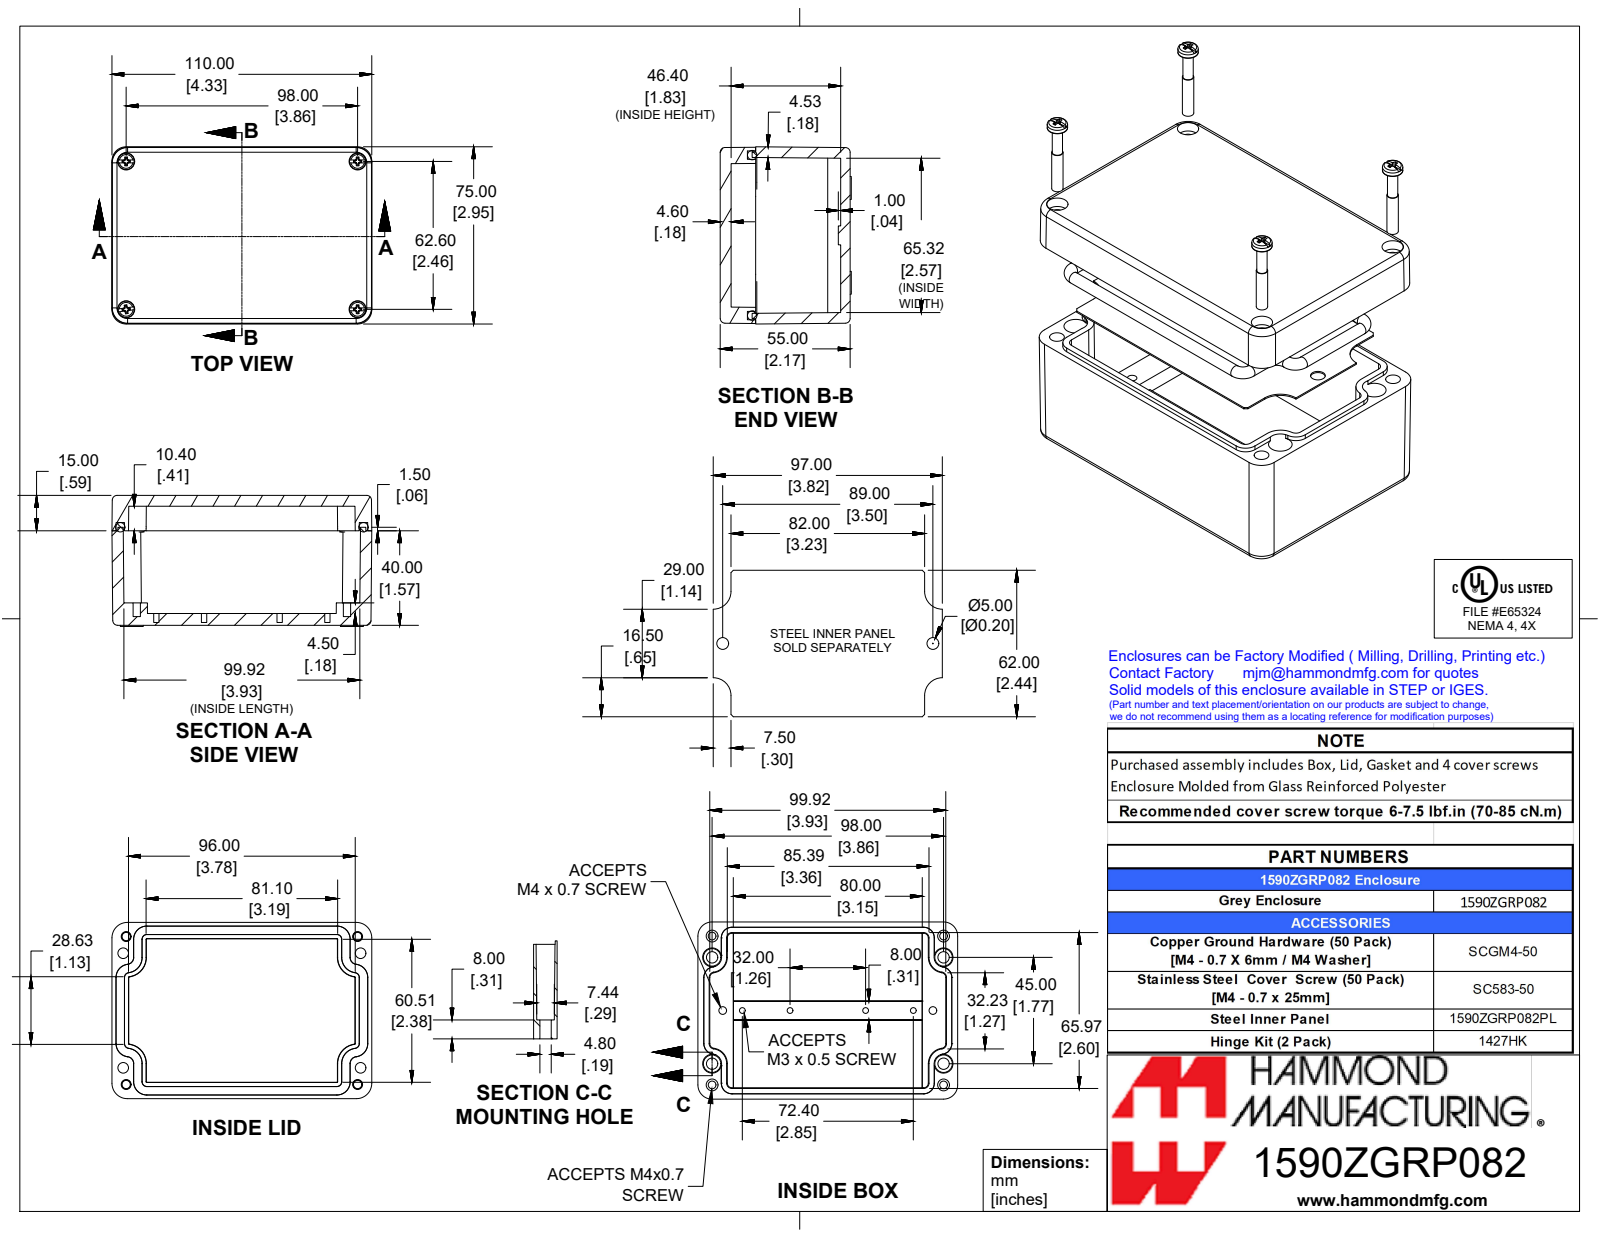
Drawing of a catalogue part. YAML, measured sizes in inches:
part_name: "1590ZGRP082"
step_written_by: "SolidWorks 2019 (CONFIG_CONTROL_DESIGN)"
units: inches
bodies: {solids: 8, faces: 465, planar: 257, cylindrical: 88, other: 120}
overall_size: [4.331, 2.953, 2.185]
volume: 10.62
surface_area: 142.6
round_holes:
  - {diameter: 0.128, count: 6}
  - {diameter: 0.197, count: 6}
  - {diameter: 0.097, count: 4}
  - {diameter: 0.138, count: 4}
  - {diameter: 0.177, count: 4}
  - {diameter: 0.189, count: 4}
  - {diameter: 0.283, count: 4}
round_bosses_or_shafts:
  - {diameter: 0.157, count: 6}
  - {diameter: 0.272, count: 4}
  - {diameter: 0.152, count: 4}
  - {diameter: 0.137, count: 4}
partial_cylinders:
  - {radius: 0.039, count: 16}
  - {radius: 0.079, count: 8}
  - {radius: 0.236, count: 4}
  - {radius: 0.256, count: 4}
  - {radius: 0.295, count: 4}
face_to_face_distances: [2.165, 0.374, 1.791, 0.178, 0.394, 0.02, 1.772, 1.984, 1.61, 1.591]
hole_center_spacings: [3.858, 0.085, 0.282, 0.29, 0.346, 0.354, 0.904, 0.981]
